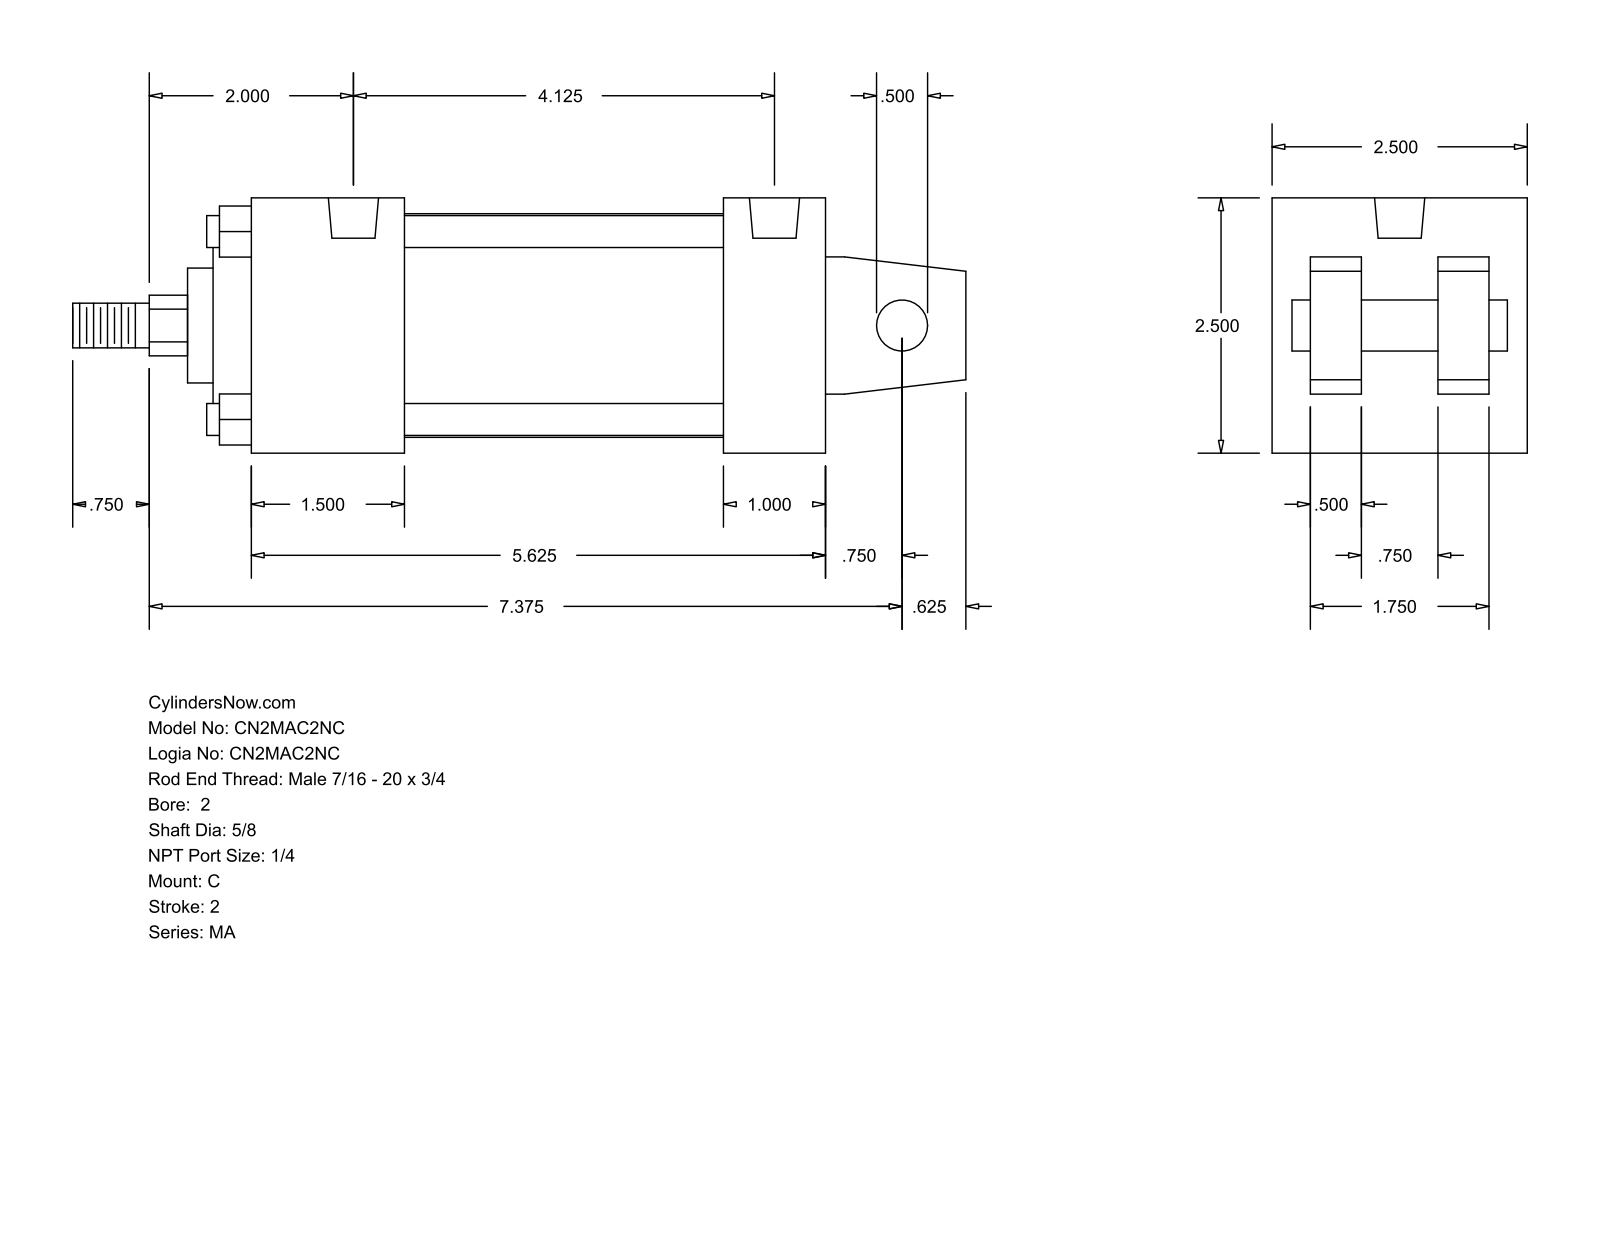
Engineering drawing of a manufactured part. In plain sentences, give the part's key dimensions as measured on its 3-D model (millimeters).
The part is named "MA_C__0200_0.625". Its 3-D file was written by "GSSL Pune (CONFIG_CONTROL_DESIGN)". It is 0 solids with 105 faces: 77 planar, 28 cylindrical and 0 other. Overall it measures 222.25 by 63.5 by 63.5 millimeters. Round holes: 4 of diameter 7.94, 2 of diameter 12.49. Round bosses or shafts: 4 of diameter 7.94, 1 of diameter 55.63, 1 of diameter 50.8, 1 of diameter 28.57, 1 of diameter 15.88, 1 of diameter 12.7, 1 of diameter 11.11. Partial cylindrical surfaces (rounded edges, fillets, slot ends): 1 of radius 7.54. The main face-to-face distances are 63.5, 9.52, 12.7, 22.22, 41.28, 53.98, 31.76, 25.4, 38.1, 142.88. The hole center spacings are 104.77.
